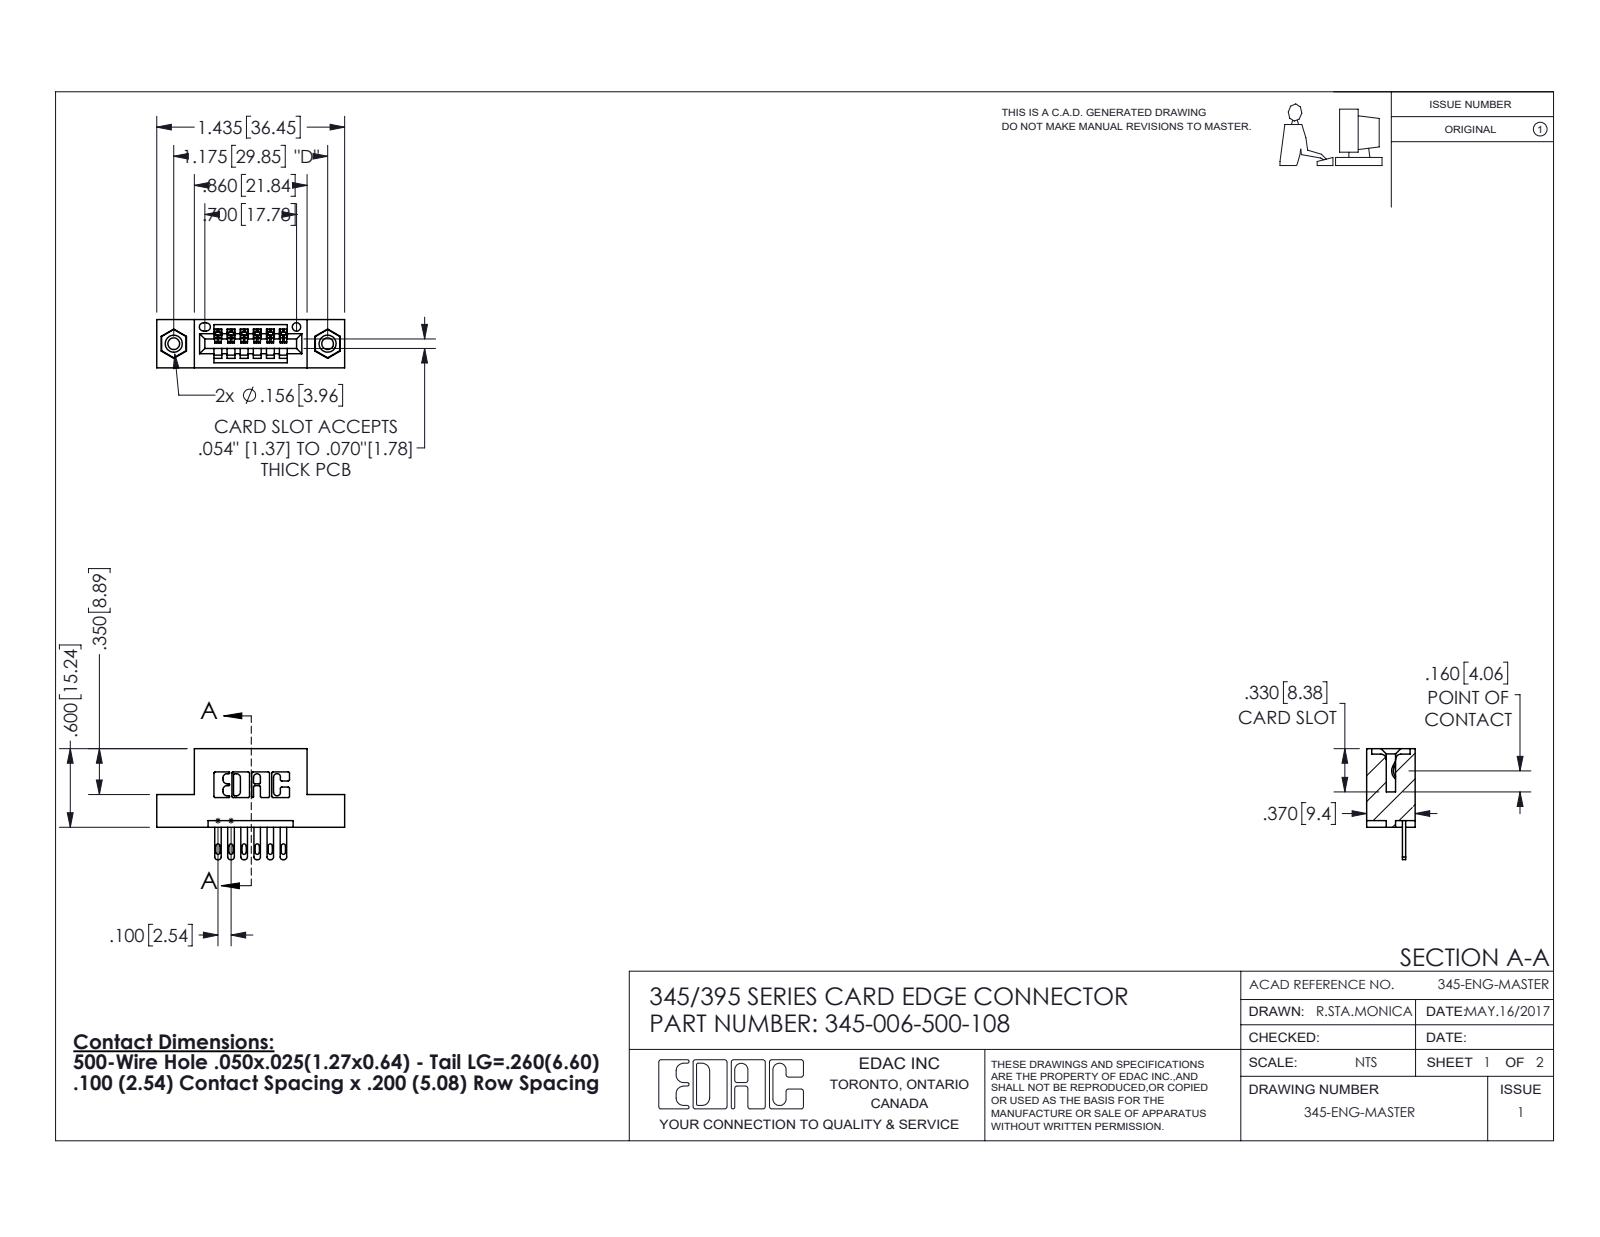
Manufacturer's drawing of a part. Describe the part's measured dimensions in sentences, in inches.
The part is named "345-250-001_345-250-003-102; 345-292-001_345-293-100; 345 Part_Flush Mounting Lugs - 0.156 Dia-TI; 345-006-500-108". Its 3-D file was written by "SolidWorks 2016 (CONFIG_CONTROL_DESIGN)". It is 9 solids with 510 faces: 316 planar, 178 cylindrical and 16 other. Overall it measures 1.435 by 0.847 by 0.37 inches. Its volume is 0.193 cubic inches and its surface area 5.81 square inches. Round holes: 2 of diameter 0.089, 2 of diameter 0.125, 2 of diameter 0.156, 1 of diameter 0.064. Round bosses or shafts: 2 of diameter 0.155. Partial cylindrical surfaces (rounded edges, fillets, slot ends): 22 of radius 0.01, 12 of radius 0.006, 12 of radius 0.016, 12 of radius 0.02, 6 of radius 0.007, 6 of radius 0.031, 3 of radius 0.026, 2 of radius 0.031. The main face-to-face distances are 0.2, 0.37, 0.072, 0.298, 0.1, 0.098, 0.272, 0.025, 0.06, 0.3. The hole center spacings are 0.27, 0.946, 1.175.
